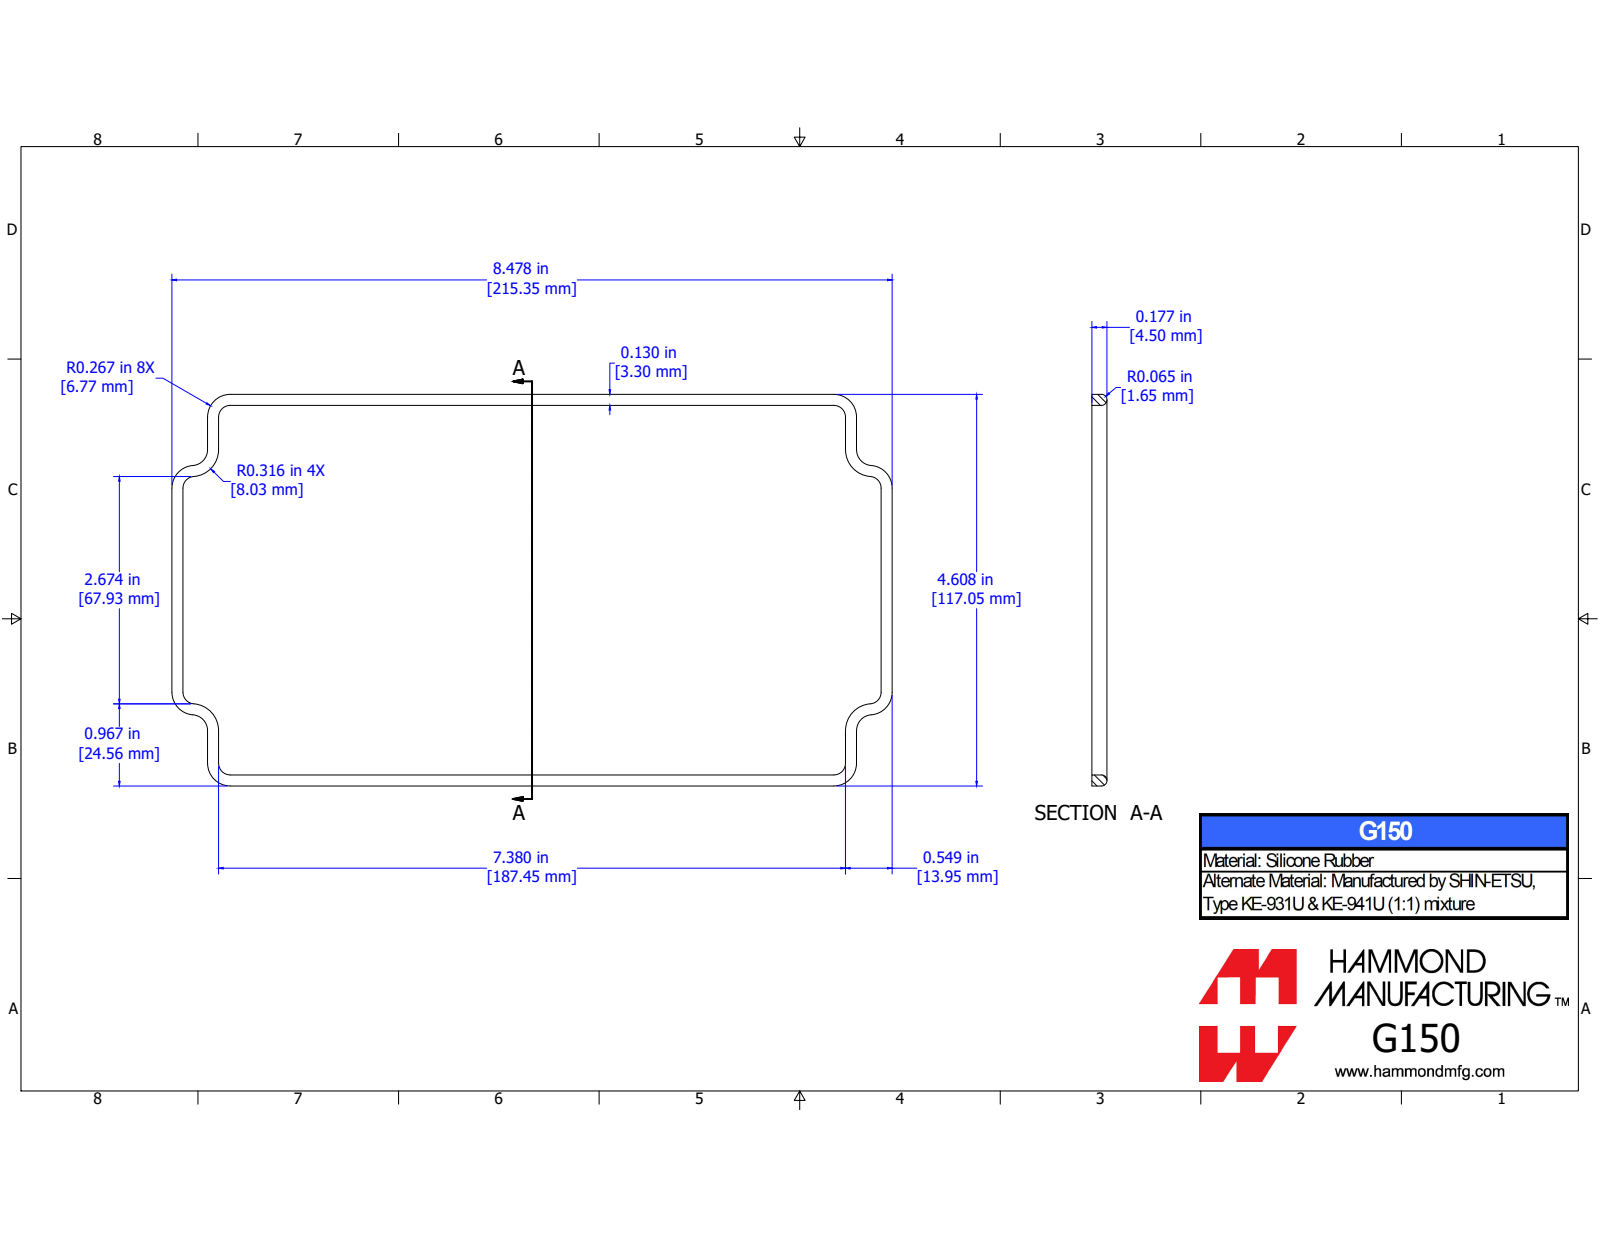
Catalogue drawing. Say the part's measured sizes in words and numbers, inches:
The part is named "1590Z150G". Its 3-D file was written by "SolidWorks 2019 (CONFIG_CONTROL_DESIGN)". It is 1 solid with 82 faces: 18 planar, 16 cylindrical and 48 other. Overall it measures 8.512 by 4.575 by 0.142 inches. Its volume is 0.395 cubic inches and its surface area 11.85 square inches. Partial cylindrical surfaces (rounded edges, fillets, slot ends): 12 of radius 0.059. The main face-to-face distances are 4.449, 8.386, 0.453, 7.933, 7.48, 0.142.
